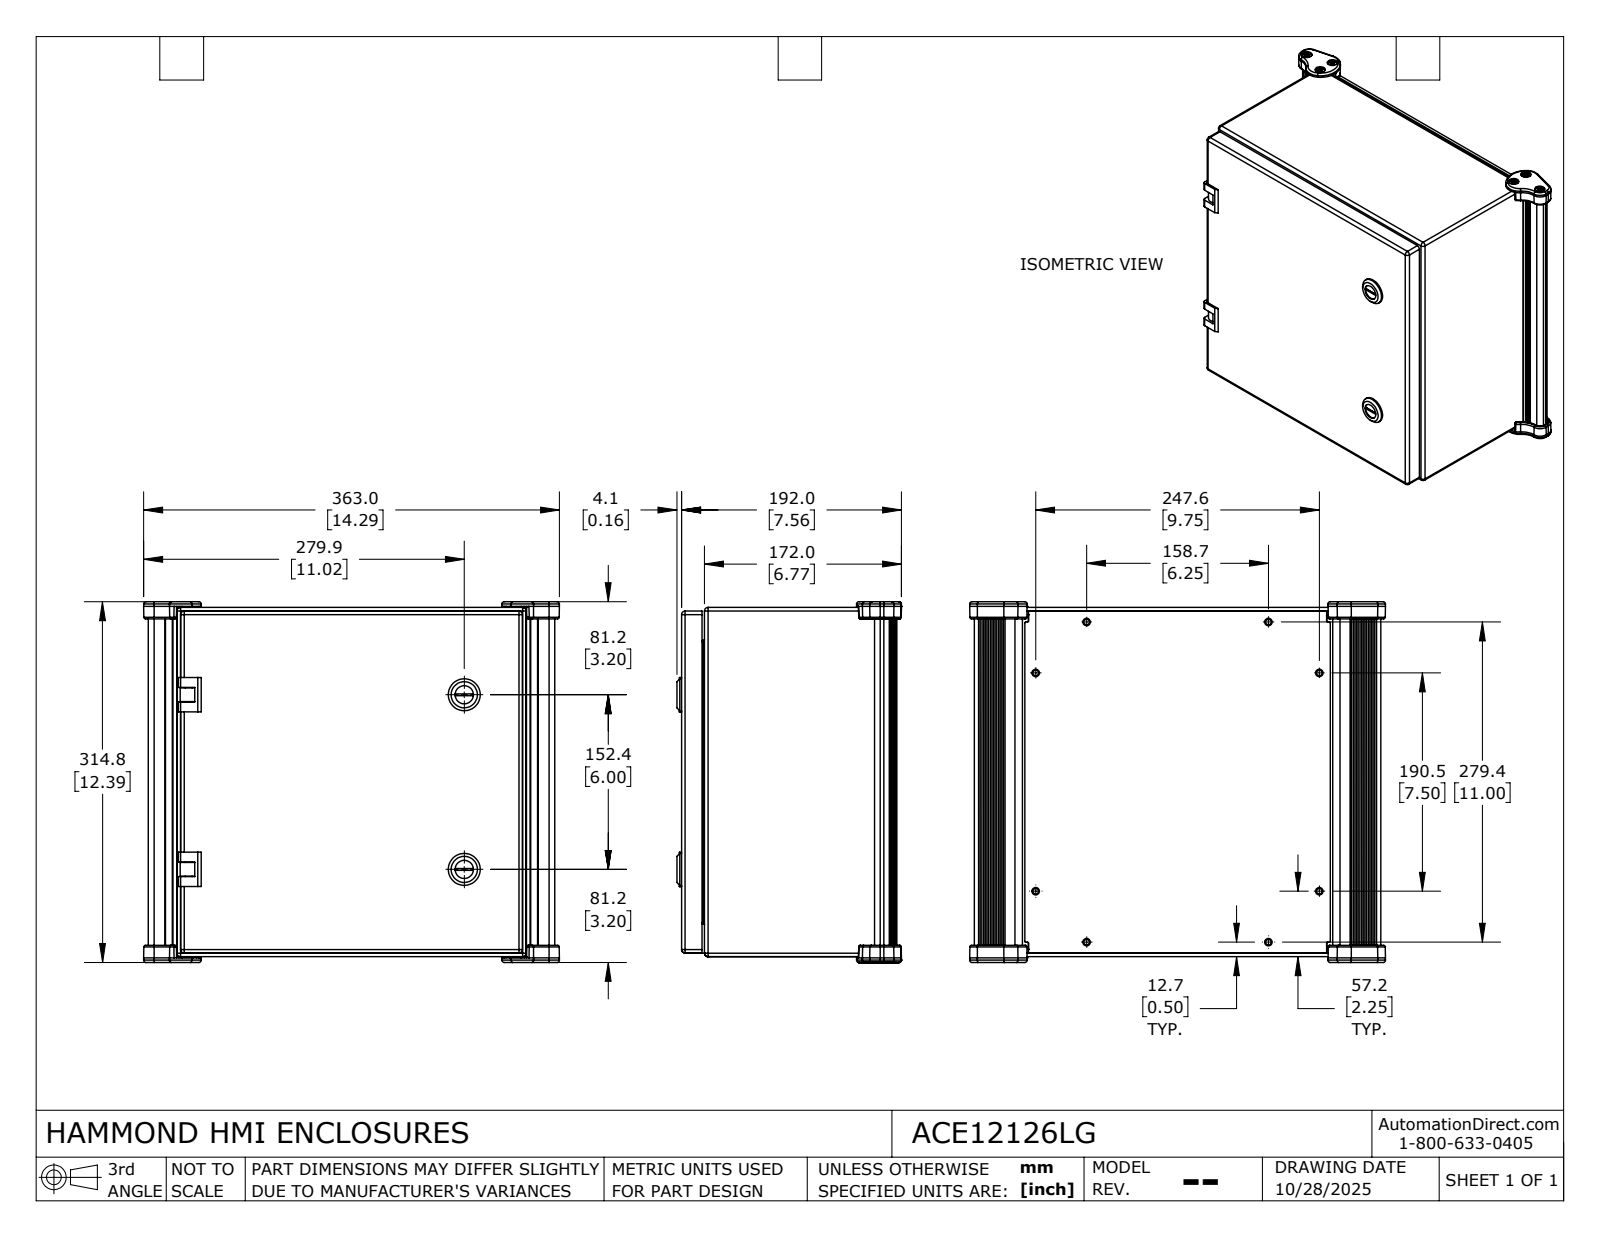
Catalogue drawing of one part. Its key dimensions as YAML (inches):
part_name: "ACE12126LG"
step_written_by: "SolidWorks 2024 (AUTOMOTIVE_DESIGN)"
units: inches
bodies: {solids: 90, faces: 2250, planar: 1037, cylindrical: 845, other: 368}
overall_size: [14.292, 12.395, 7.719]
volume: 87.4
surface_area: 1972
round_holes:
  - {diameter: 0.156, count: 12}
  - {diameter: 0.205, count: 12}
  - {diameter: 0.413, count: 12}
  - {diameter: 0.234, count: 10}
  - {diameter: 0.19, count: 8}
  - {diameter: 0.196, count: 5}
  - {diameter: 0.159, count: 4}
  - {diameter: 0.16, count: 4}
  - {diameter: 0.406, count: 4}
  - {diameter: 0.197, count: 2}
  - {diameter: 0.232, count: 2}
  - {diameter: 0.25, count: 2}
round_bosses_or_shafts:
  - {diameter: 0.19, count: 12}
  - {diameter: 0.149, count: 12}
  - {diameter: 0.25, count: 10}
  - {diameter: 0.256, count: 8}
  - {diameter: 0.236, count: 5}
  - {diameter: 0.44, count: 4}
  - {diameter: 0.375, count: 4}
  - {diameter: 0.33, count: 4}
partial_cylinders:
  - {radius: 0.01, count: 38}
  - {radius: 0.059, count: 32}
  - {radius: 0.122, count: 28}
  - {radius: 0.041, count: 20}
  - {radius: 0.016, count: 16}
  - {radius: 0.03, count: 16}
  - {radius: 0.05, count: 16}
  - {radius: 0.039, count: 14}
face_to_face_distances: [0.081, 0.125, 6.831, 11.919, 11.919, 6.912, 6.956, 7.037, 6.706, 0.125]
hole_center_spacings: [0.709, 4, 5.439, 4.743, 2.335, 5.441, 11.33, 1.19]
